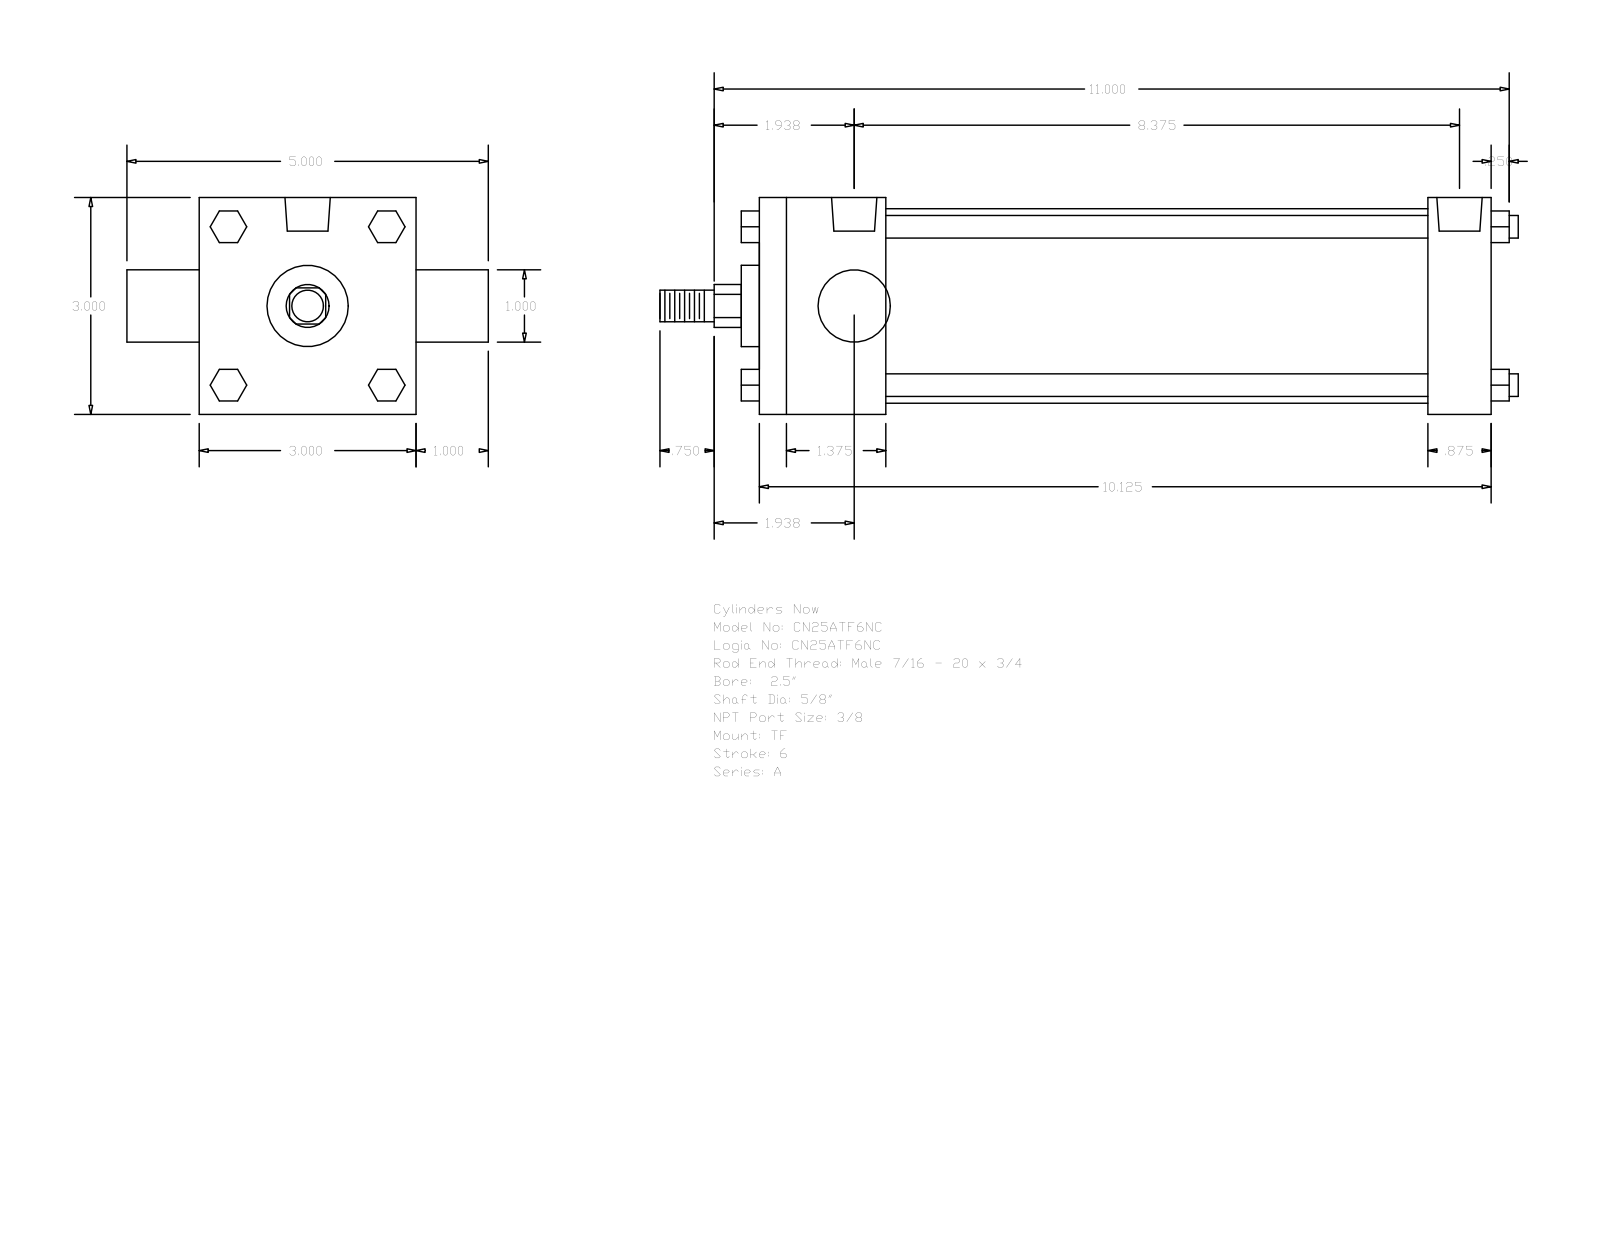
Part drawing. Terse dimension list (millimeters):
name: A_TF__0250_0.625
written by: GSSL Pune (CONFIG_CONTROL_DESIGN)
unit: mm
bodies: 0 solids, 120 faces (92 planar, 28 cylindrical, 0 other)
size: 301.62 × 127 × 76.2
holes: 3× ⌀5.56, 2× ⌀15.93
bosses: 4× ⌀7.94, 1× ⌀68.33, 1× ⌀28.57, 1× ⌀25.4, 1× ⌀15.88, 1× ⌀11.11
rounds: 1× R7.54
face distances: 76.2, 257.17, 44.45, 234.94, 190.49, 212.72, 22.23, 25.4, 101.6, 6.35
hole spacings: 2.38, 215.11, 212.73, 217.49
